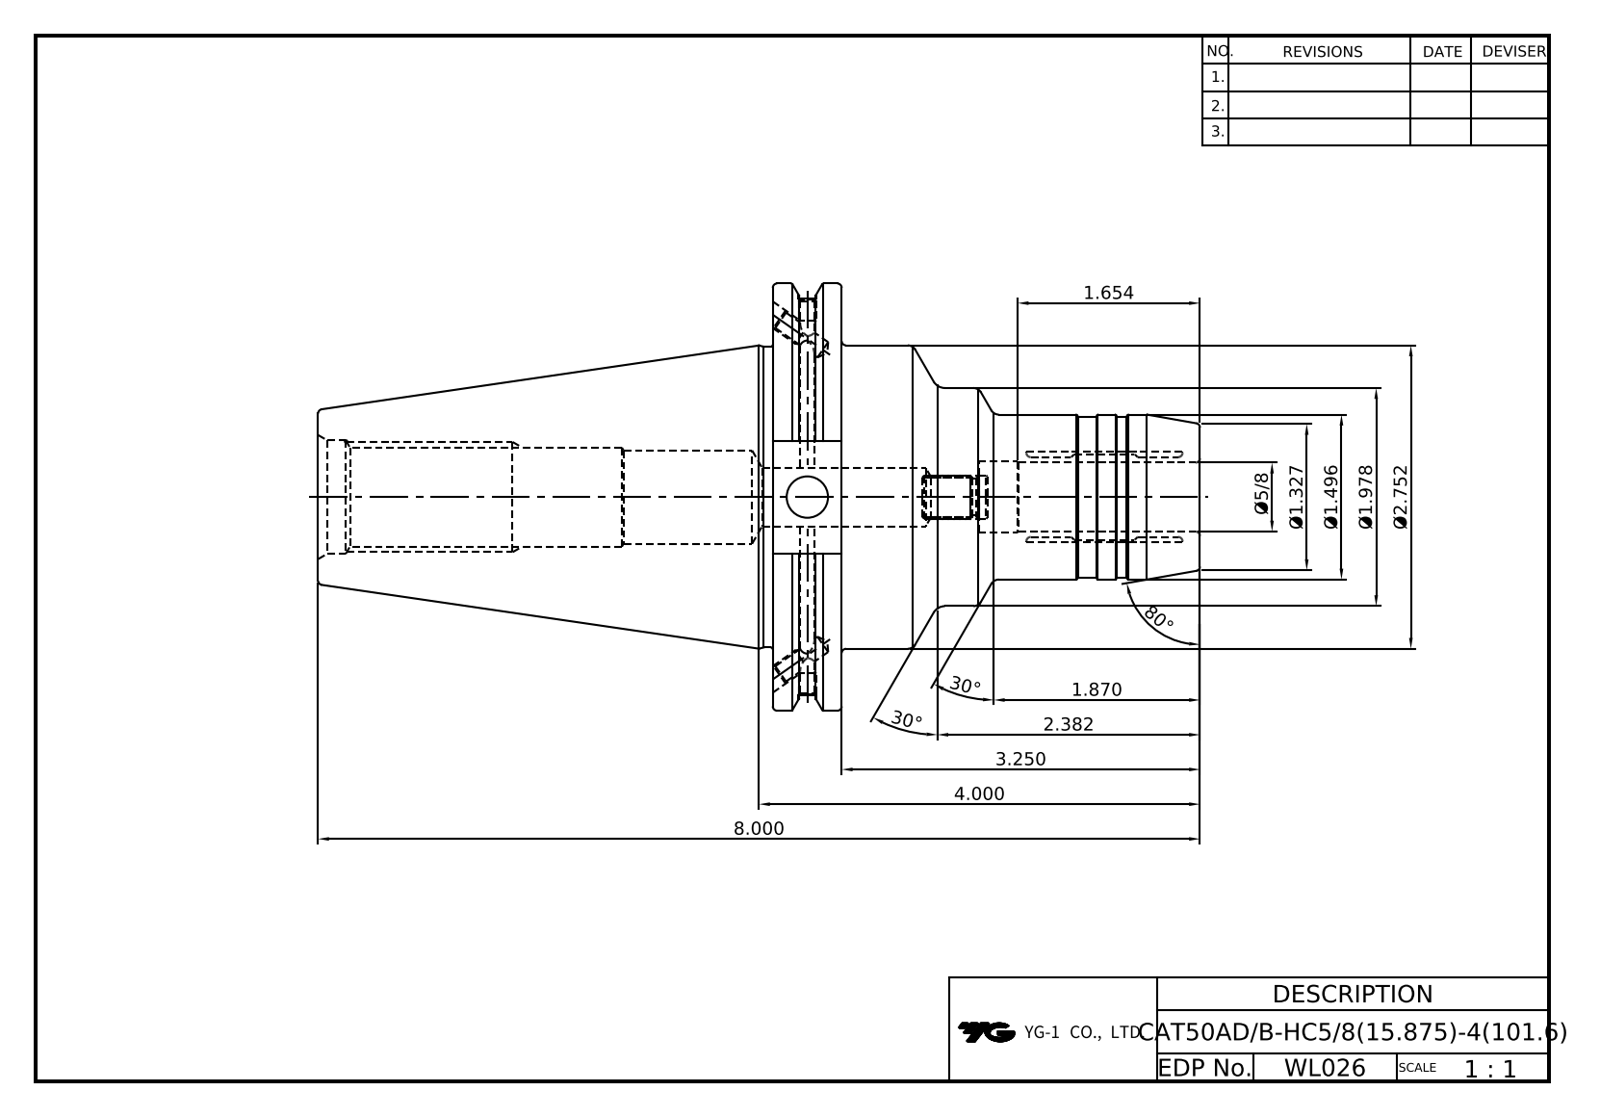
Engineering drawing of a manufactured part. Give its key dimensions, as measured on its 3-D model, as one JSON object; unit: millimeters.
{"part_name": "LO-CAT50ADB-HC15.875-101.6", "step_written_by": "Autodesk Inventor 2020 (AUTOMOTIVE_DESIGN)", "units": "millimeters", "bodies": {"solids": 1, "faces": 112, "planar": 37, "cylindrical": 34, "other": 41}, "overall_size": [203.2, 98.42, 94.69], "volume_mm3": 465575, "surface_area_mm2": 59011, "round_holes": [[3.24, 2], [4.13, 2], [4.2, 2], [5, 2], [8.92, 1], [9.53, 1], [13.5, 1], [15.87, 1], [16.4, 1], [20.5, 1], [21.97, 1], [26.2, 1]], "round_bosses_or_shafts": [[98.42, 1], [91.29, 1], [69.9, 1], [69.25, 1], [50.25, 1], [38, 1], [37, 1]], "face_to_face_distances": [15.88, 98.43, 82.55, 104.77, 120.65, 203.2, 73.03, 25.9, 110.82, 6.05]}
